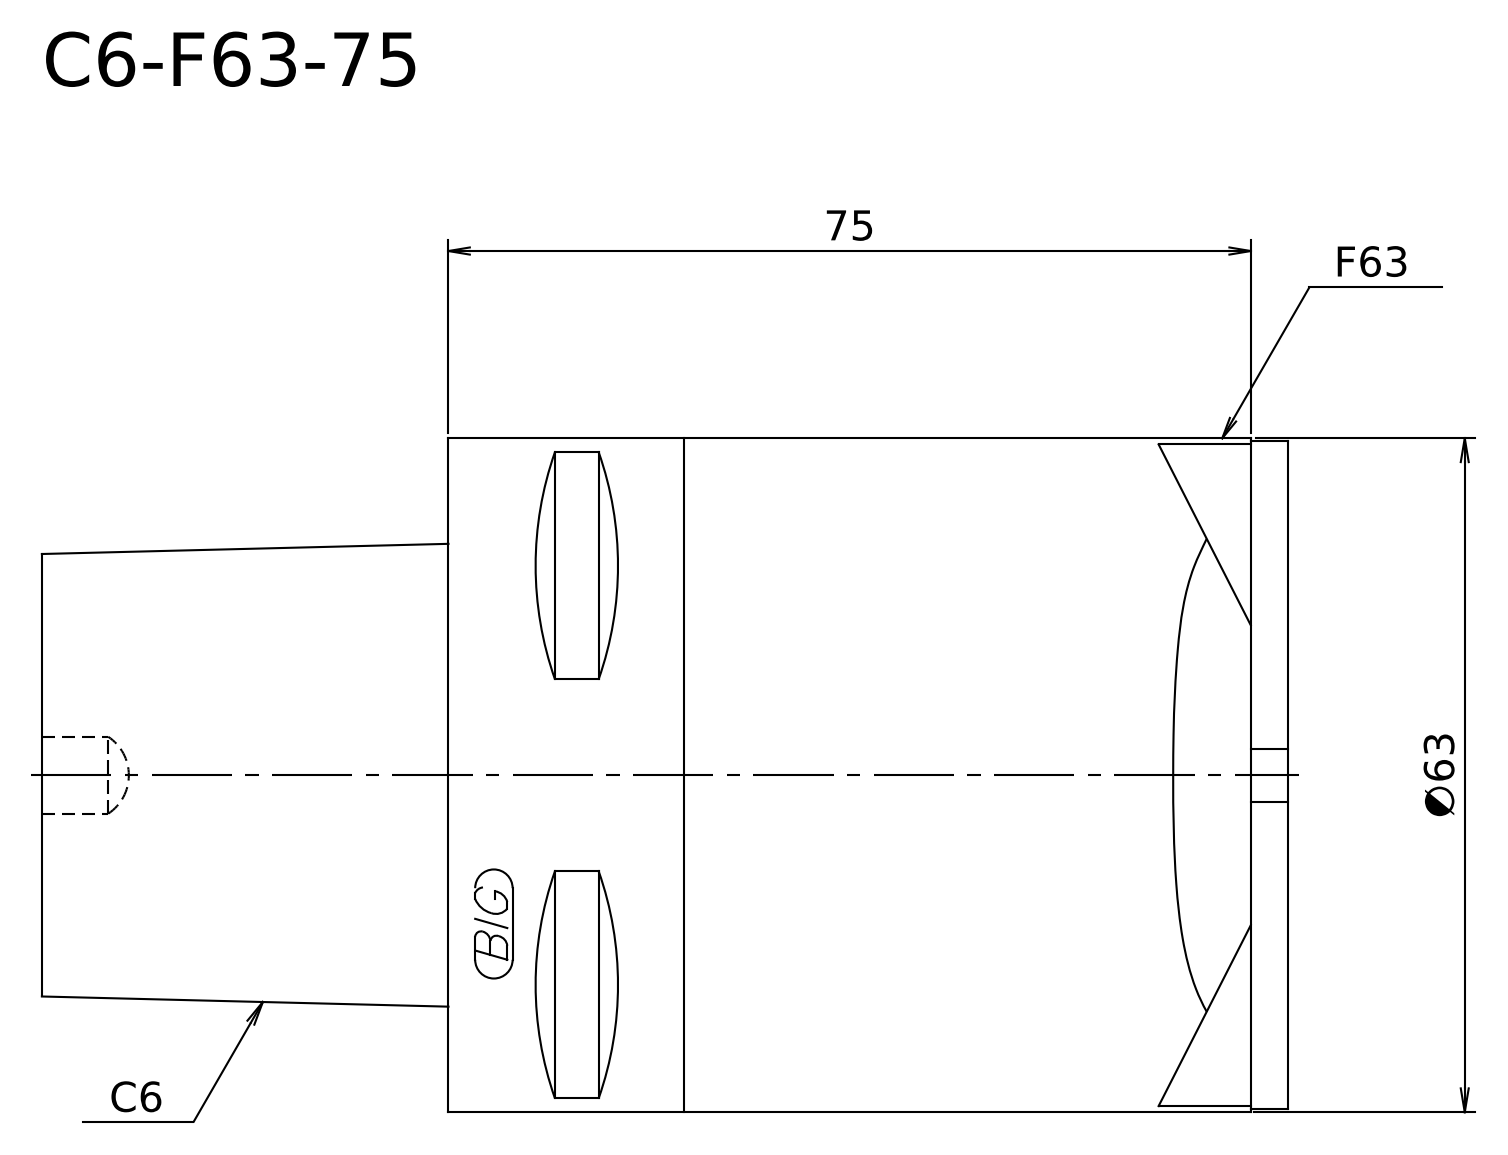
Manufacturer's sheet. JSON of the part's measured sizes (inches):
{"part_name": "C6-F63-75", "step_written_by": "SolidWorks 2021 (CONFIG_CONTROL_DESIGN)", "units": "inches", "bodies": {"solids": 1, "faces": 7, "planar": 3, "cylindrical": 2, "other": 2}, "overall_size": [4.449, 2.48, 2.48], "volume_in3": 17.53, "surface_area_in2": 40.31, "round_bosses_or_shafts": [[2.48, 1]], "face_to_face_distances": [2.953, 1.496, 4.449]}
